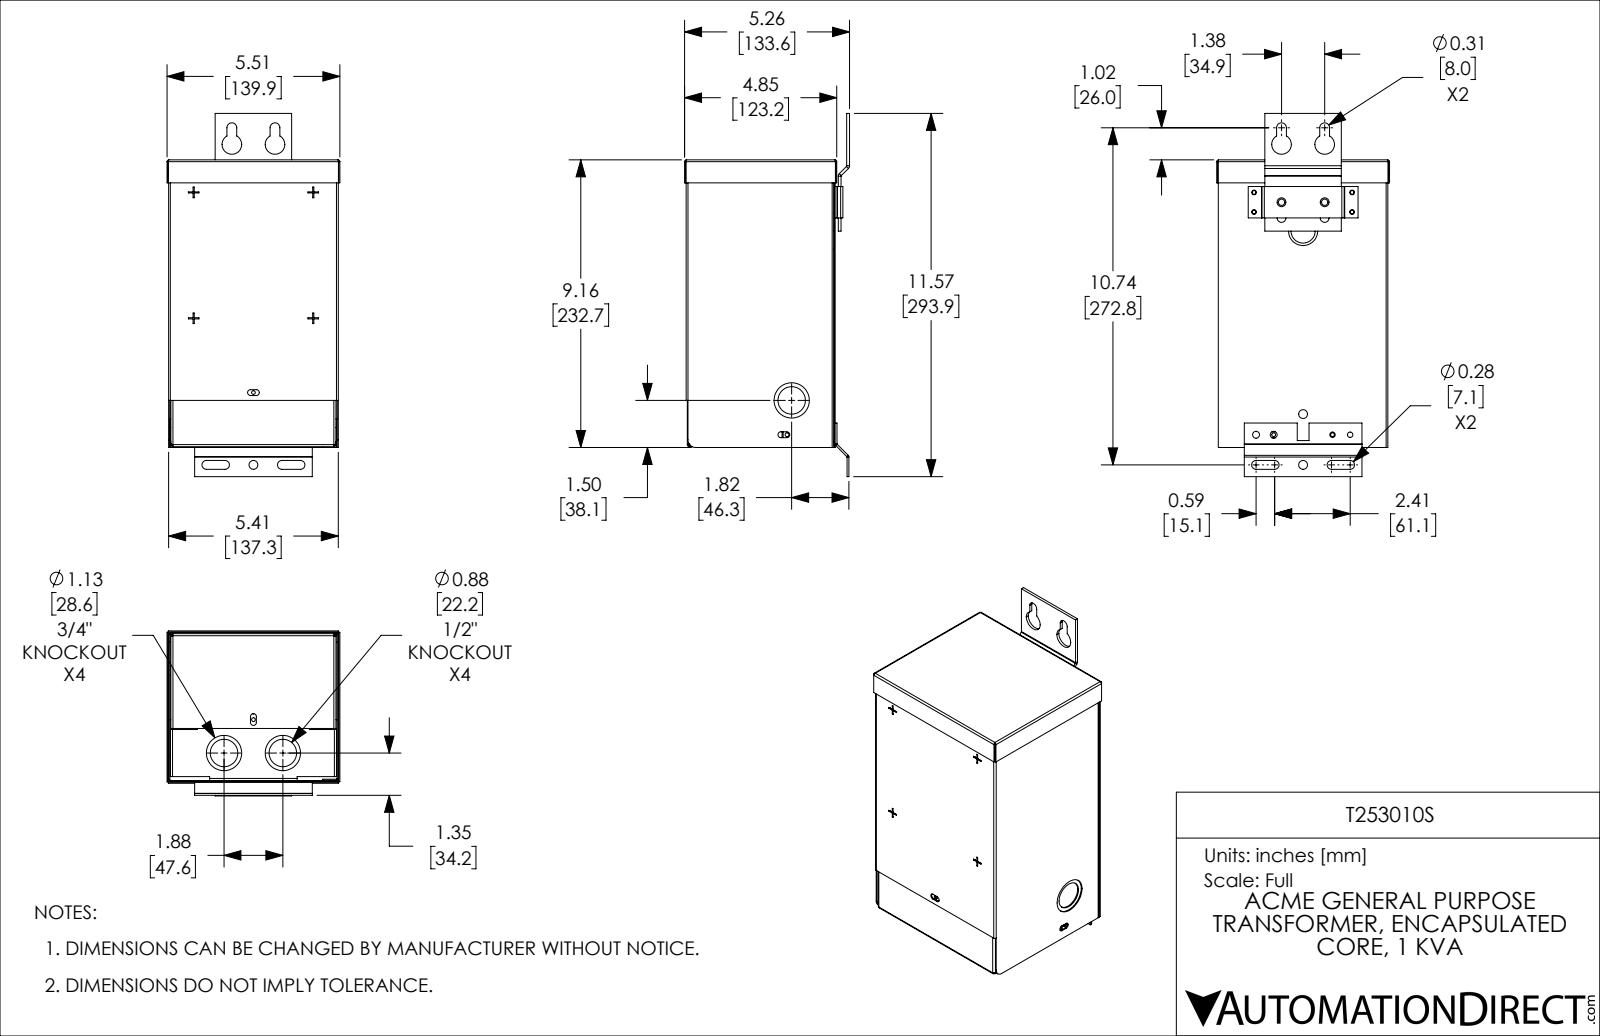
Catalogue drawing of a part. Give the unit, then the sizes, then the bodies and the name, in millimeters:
Units: millimetres
Overall size (bounding box): 293.87 × 139.9 × 133.57
Round holes (diameter × count): ⌀7.14 ×6, ⌀3.05 ×5, ⌀22.22 ×3, ⌀28.57 ×3, ⌀4.37 ×2, ⌀4.76 ×2, ⌀5.11 ×2, ⌀5.56 ×2, ⌀15.88 ×2
Round bosses / shafts (diameter × count): ⌀29.79 ×1, ⌀23.44 ×1
Partial cylindrical surfaces — rounded edges, fillets, slot ends (radius × count): R0.51 ×10, R2.38 ×10, R0.79 ×8, R1.42 ×8, R1.7 ×8, R0.38 ×4, R1.9 ×4, R3.57 ×4
Main face-to-face distances: 0.91, 119.74, 136.41, 118.83, 135.5, 137.32, 120.65, 231.14, 1.29, 2.2
Hole centre spacings: 34.92, 12.7, 14.29, 29.09, 34.08, 35.98, 37.16, 41.6
Volume: 177 414 mm³ · Surface area: 368 059 mm²
Bodies: 7 solids, 521 faces (329 planar, 152 cylindrical, 40 other)
Part name (STEP PRODUCT): T253010S
STEP written by: SolidWorks 2021 (CONFIG_CONTROL_DESIGN)
